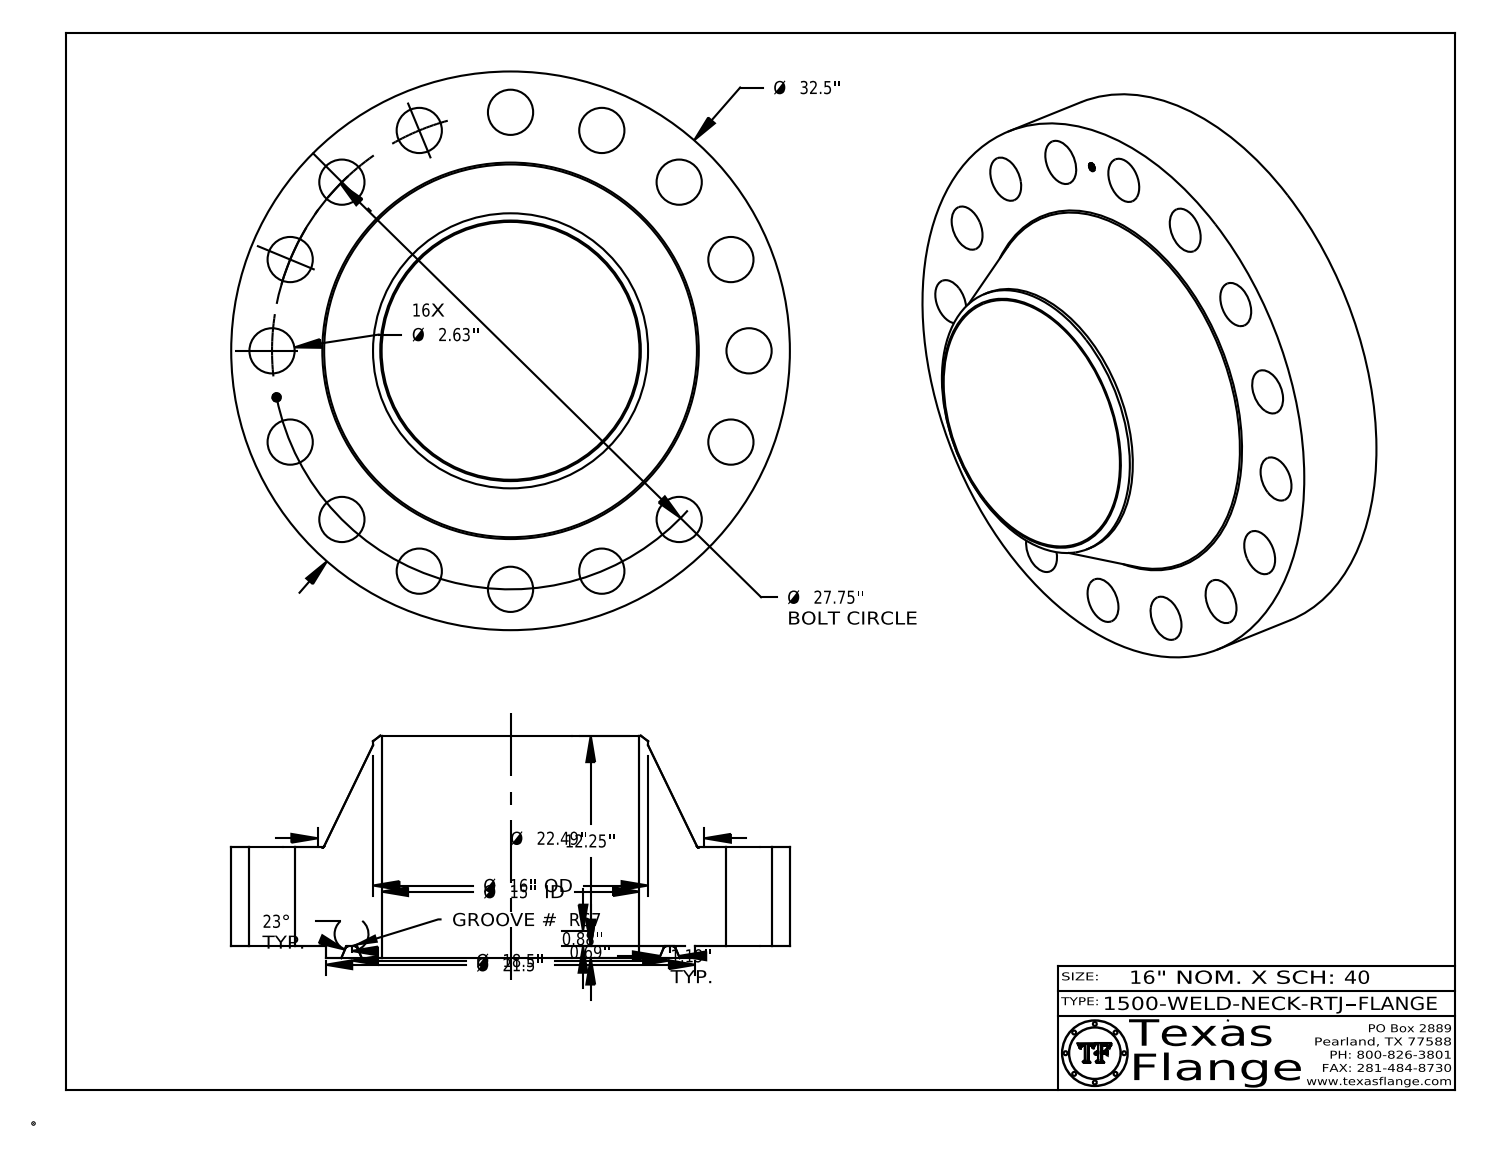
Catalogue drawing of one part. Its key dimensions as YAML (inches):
part_name: "1500-WELD-NECK-RTJ"
step_written_by: "CATIA V5 STEP AP214 (AUTOMOTIVE_DESIGN)"
units: inches
bodies: {solids: 1, faces: 445, planar: 371, cylindrical: 60, other: 14}
overall_size: [32.5, 32.5, 12.938]
volume: 3982
surface_area: 3424
round_holes:
  - {diameter: 2.63, count: 16}
  - {diameter: 0.495, count: 1}
  - {diameter: 15, count: 1}
round_bosses_or_shafts:
  - {diameter: 0.03, count: 8}
  - {diameter: 32.5, count: 1}
  - {diameter: 21.5, count: 1}
  - {diameter: 16, count: 1}
  - {diameter: 0.39, count: 1}
face_to_face_distances: [5.75, 0.688, 6.438, 12.938, 12.25, 6.5, 0.015, 6.423, 5.735, 6.515]
hole_center_spacings: [5.414, 15.417, 25.638, 27.217, 10.62, 13.875, 19.622, 23.073]
